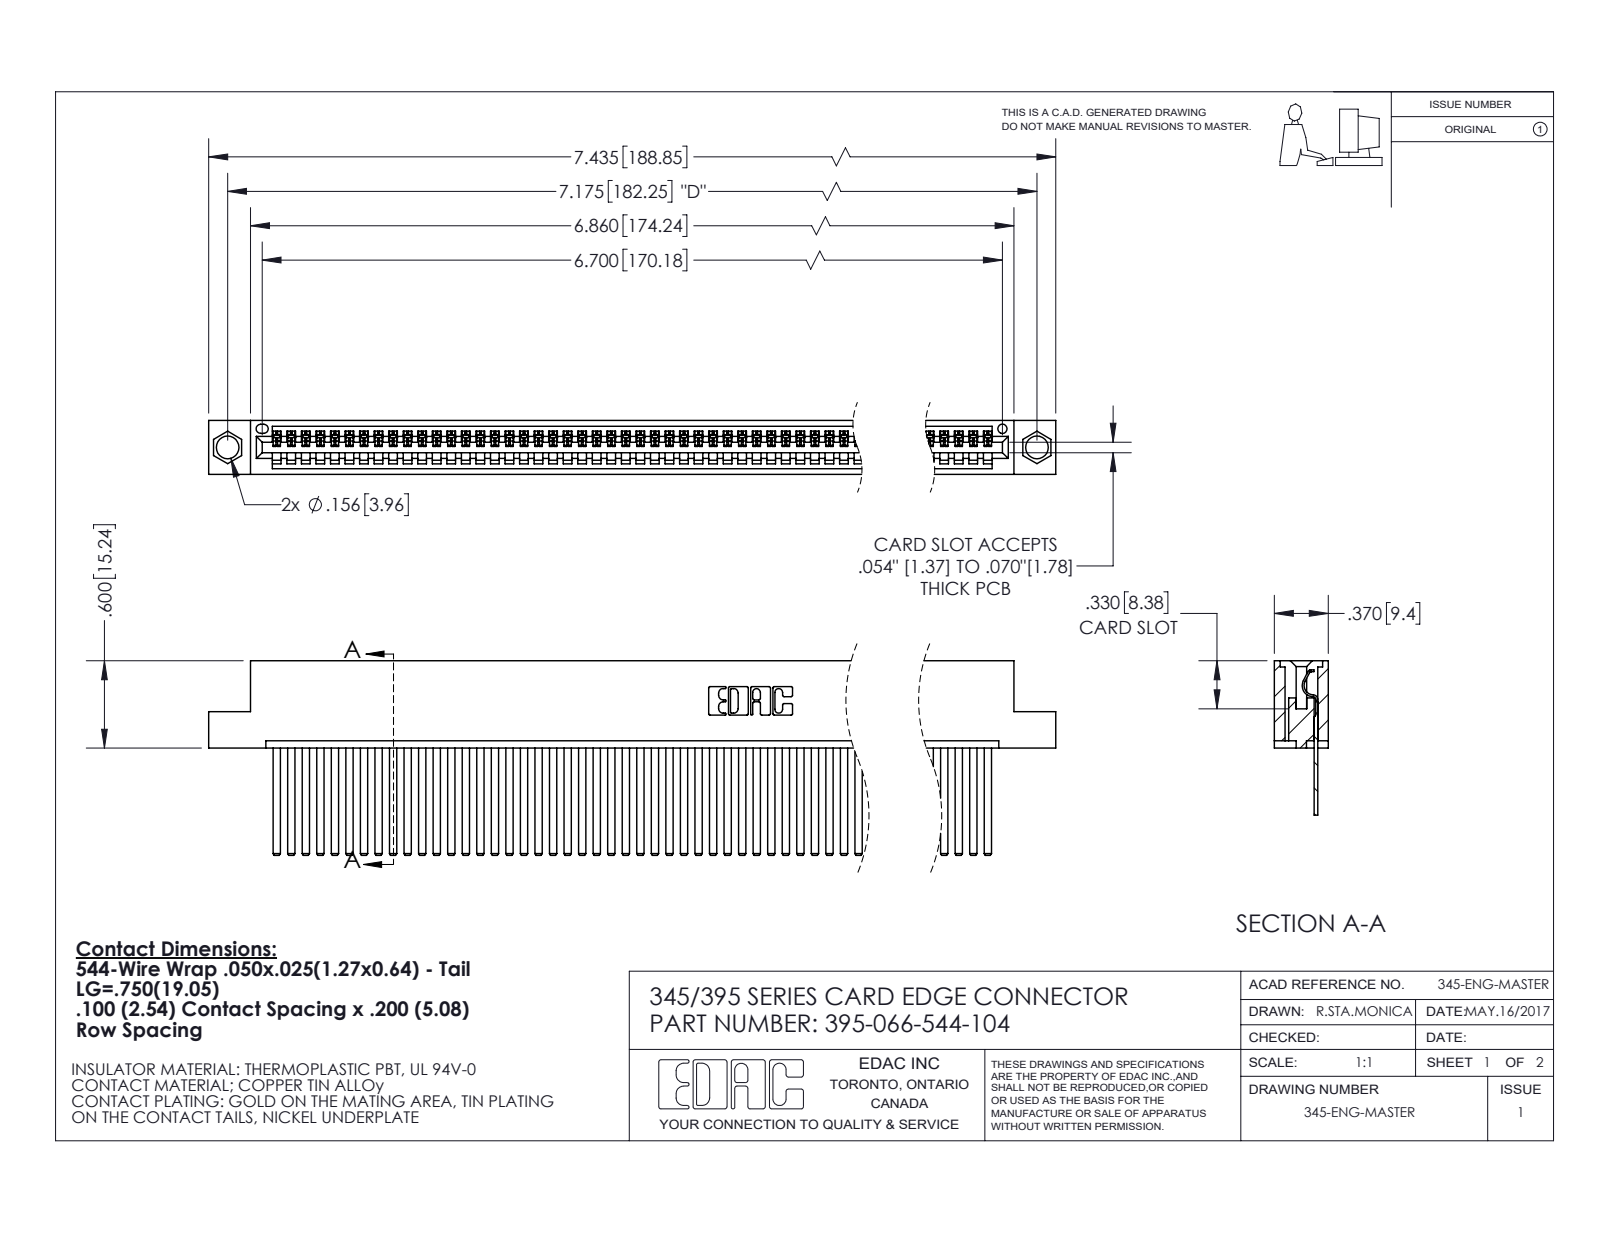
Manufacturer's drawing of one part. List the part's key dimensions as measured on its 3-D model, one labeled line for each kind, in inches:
Part name (STEP PRODUCT): 395-066-544-104; 345 Part_Flush Mounting Lugs - 0.156 Dia-TI; 345-292-001_345-293-144
STEP written by: SolidWorks 2020 (CONFIG_CONTROL_DESIGN)
Units: inches
Bodies: 67 solids, 3572 faces (2470 planar, 1102 cylindrical, 0 other)
Overall size (bounding box): 7.435 × 1.337 × 0.37
Volume: 1.147 in³ · Surface area: 42.53 in²
Round holes (diameter × count): ⌀0.156 ×2, ⌀0.064 ×1
Partial cylindrical surfaces — rounded edges, fillets, slot ends (radius × count): R0.006 ×132, R0.01 ×22, R0.007 ×6, R0.031 ×6, R0.026 ×3, R0.031 ×2, R0.04 ×2, R0.014 ×1
Main face-to-face distances: 0.072, 0.298, 0.025, 0.098, 0.272, 0.37, 0.2, 0.225, 0.149, 0.072
Hole centre spacings: 0.27, 6.939, 7.175
